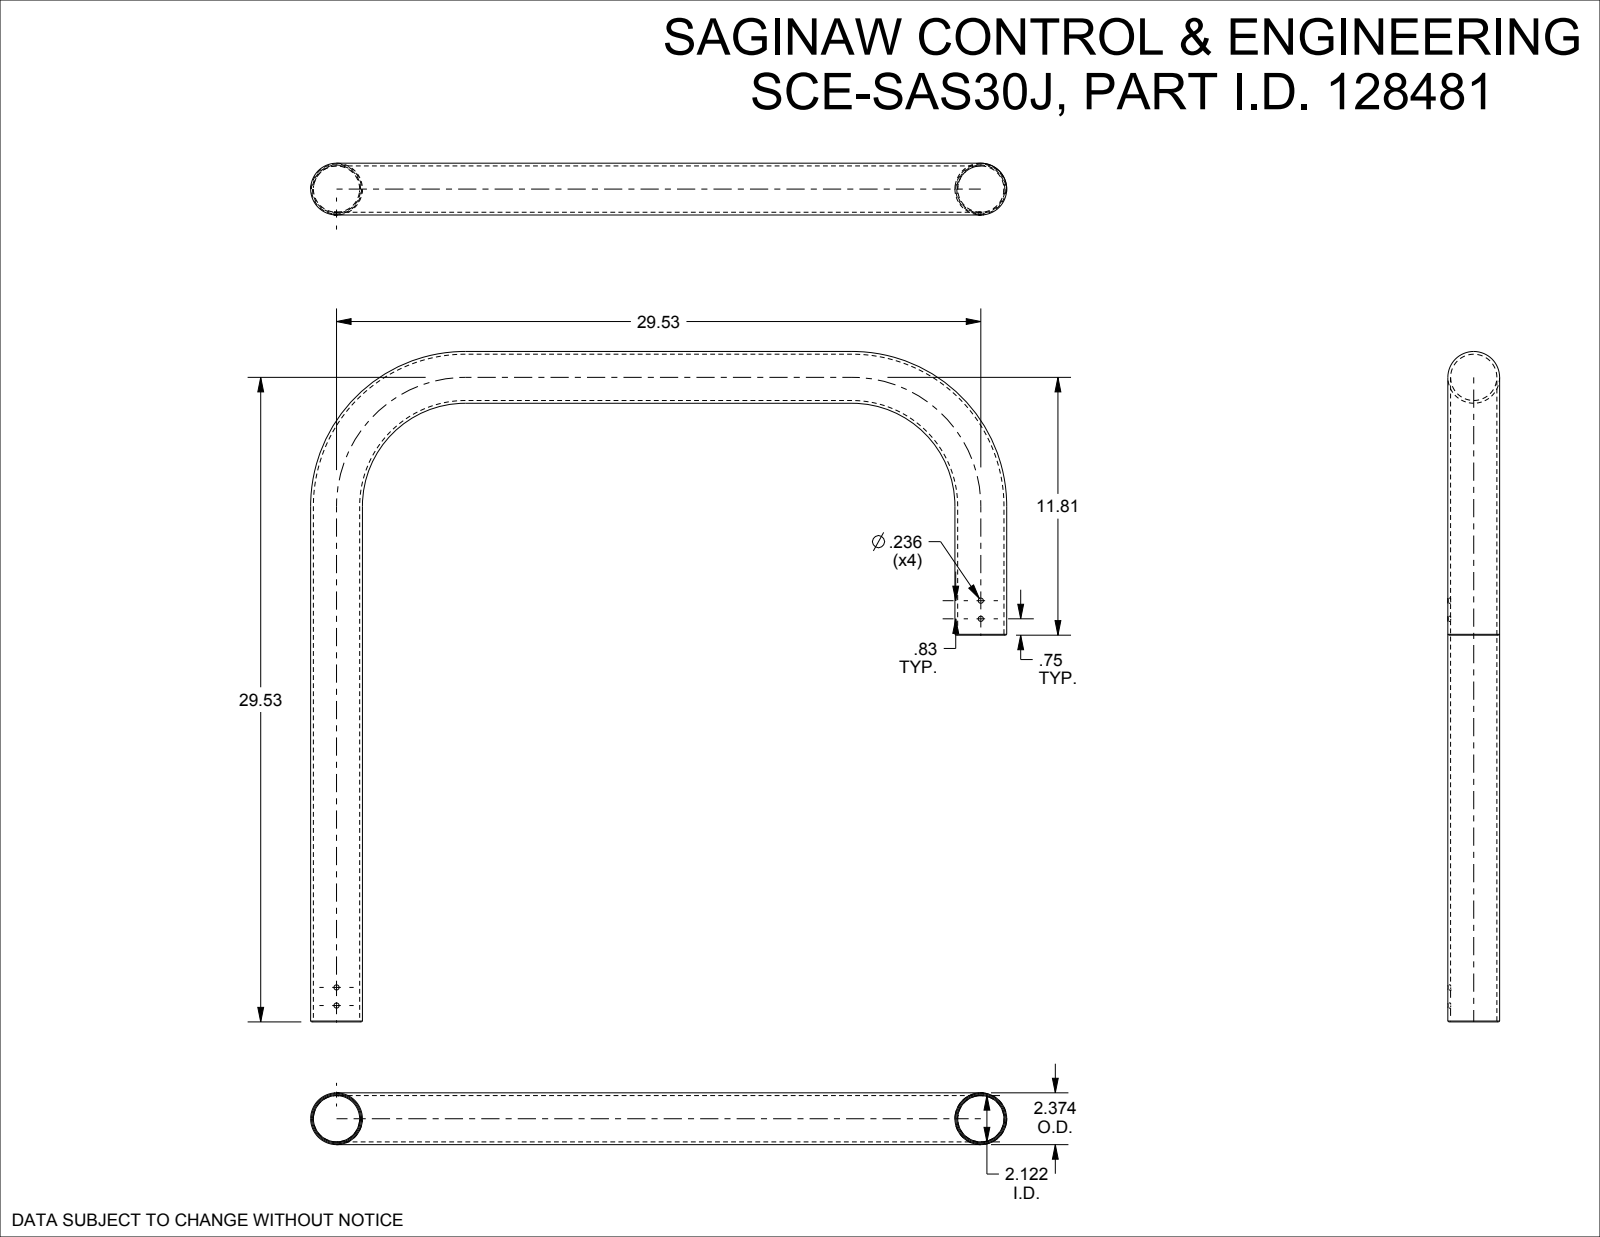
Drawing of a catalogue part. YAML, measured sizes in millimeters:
part_name: "SCE-SAS30J"
step_written_by: "SolidWorks 2023 (AUTOMOTIVE_DESIGN)"
units: millimeters
bodies: {solids: 1, faces: 38, planar: 2, cylindrical: 8, other: 28}
overall_size: [810.4, 780.1, 60.3]
volume: 957700
surface_area: 600000
round_holes:
  - {diameter: 6, count: 4}
face_to_face_distances: [450]
hole_center_spacings: [21.1, 21.1, 864, 874.7, 874.7, 885.7]
